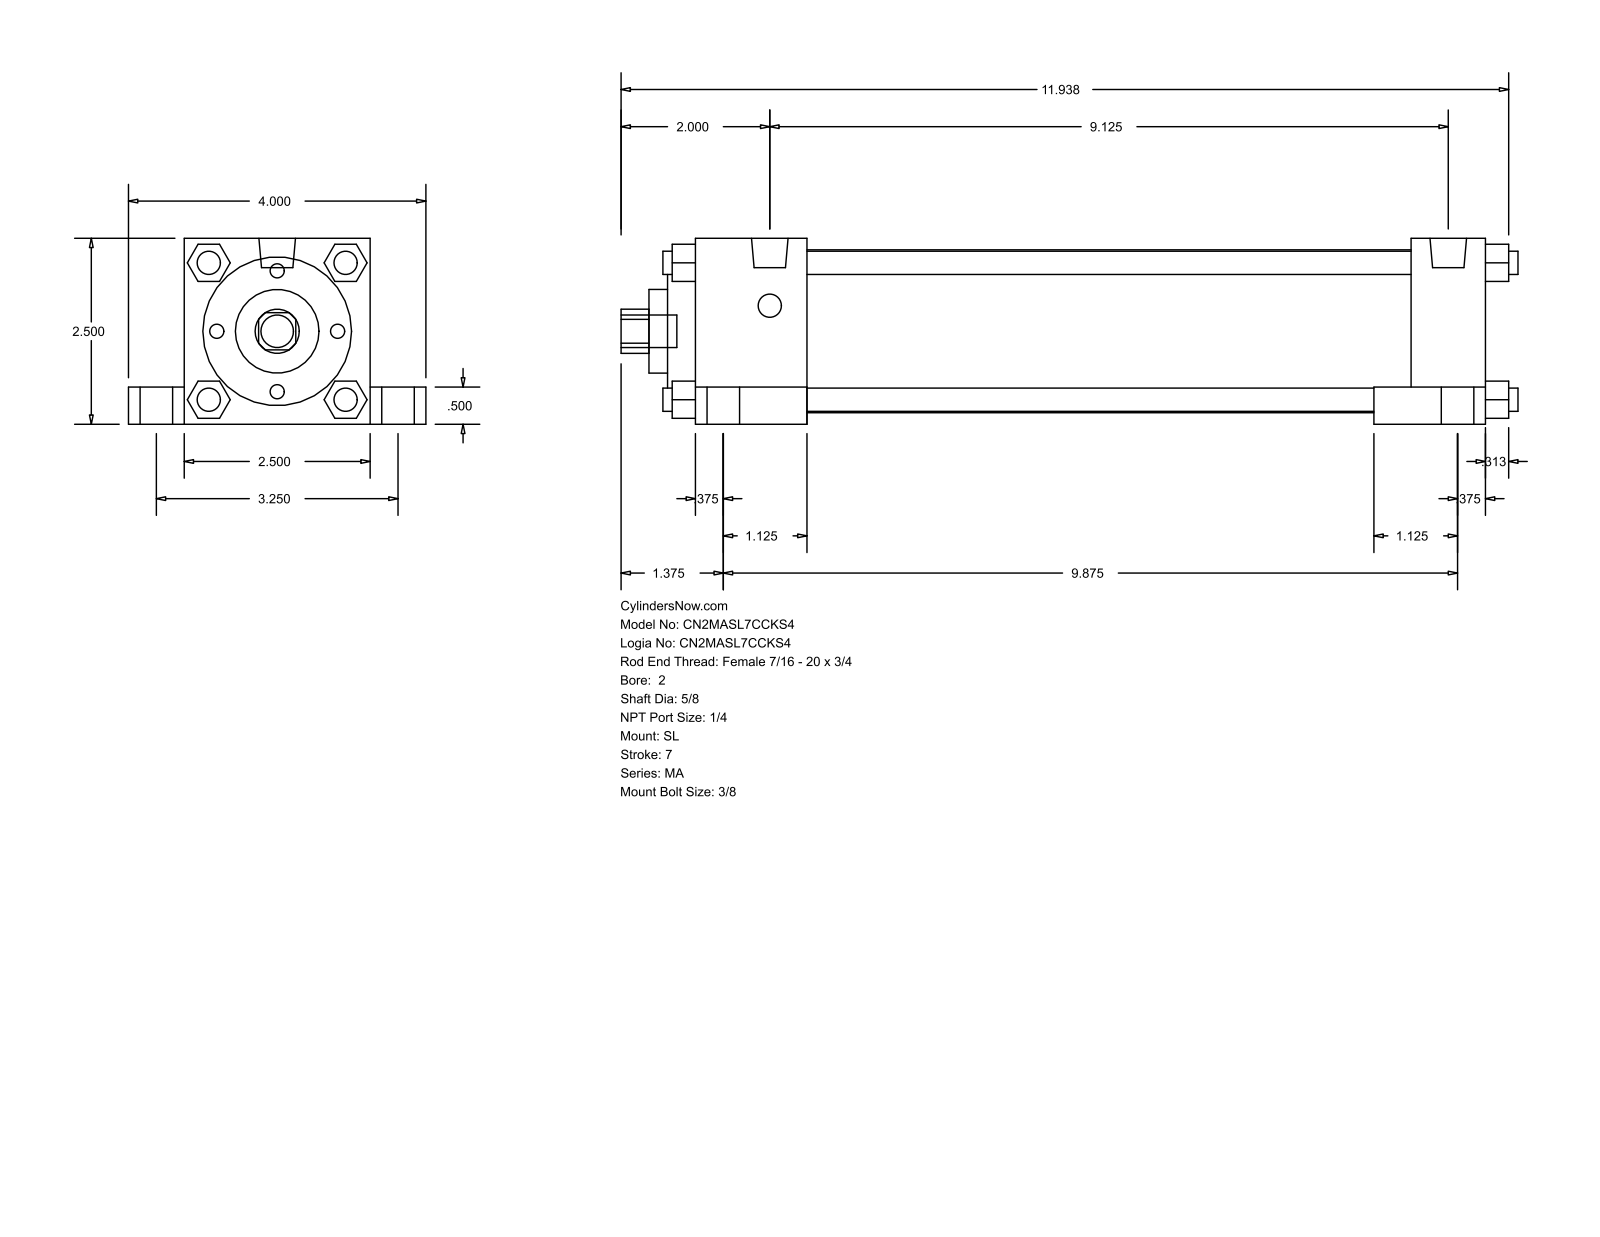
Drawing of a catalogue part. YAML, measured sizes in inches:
part_name: "MA_SL__0200_0.625"
step_written_by: "GSSL Pune (CONFIG_CONTROL_DESIGN)"
units: inches
bodies: {solids: 0, faces: 150, planar: 113, cylindrical: 37, other: 0}
overall_size: [12.063, 4, 2.5]
round_holes:
  - {diameter: 0.625, count: 1}
  - {diameter: 1.125, count: 1}
  - {diameter: 2, count: 1}
  - {diameter: 2.19, count: 1}
round_bosses_or_shafts:
  - {diameter: 0.313, count: 8}
  - {diameter: 0.437, count: 5}
  - {diameter: 0.687, count: 4}
  - {diameter: 0.492, count: 2}
partial_cylinders:
  - {radius: 0.297, count: 1}
face_to_face_distances: [2.5, 0.5, 0.375, 0.75, 3.25, 1.5, 2, 10.625, 9.125, 9.625]
